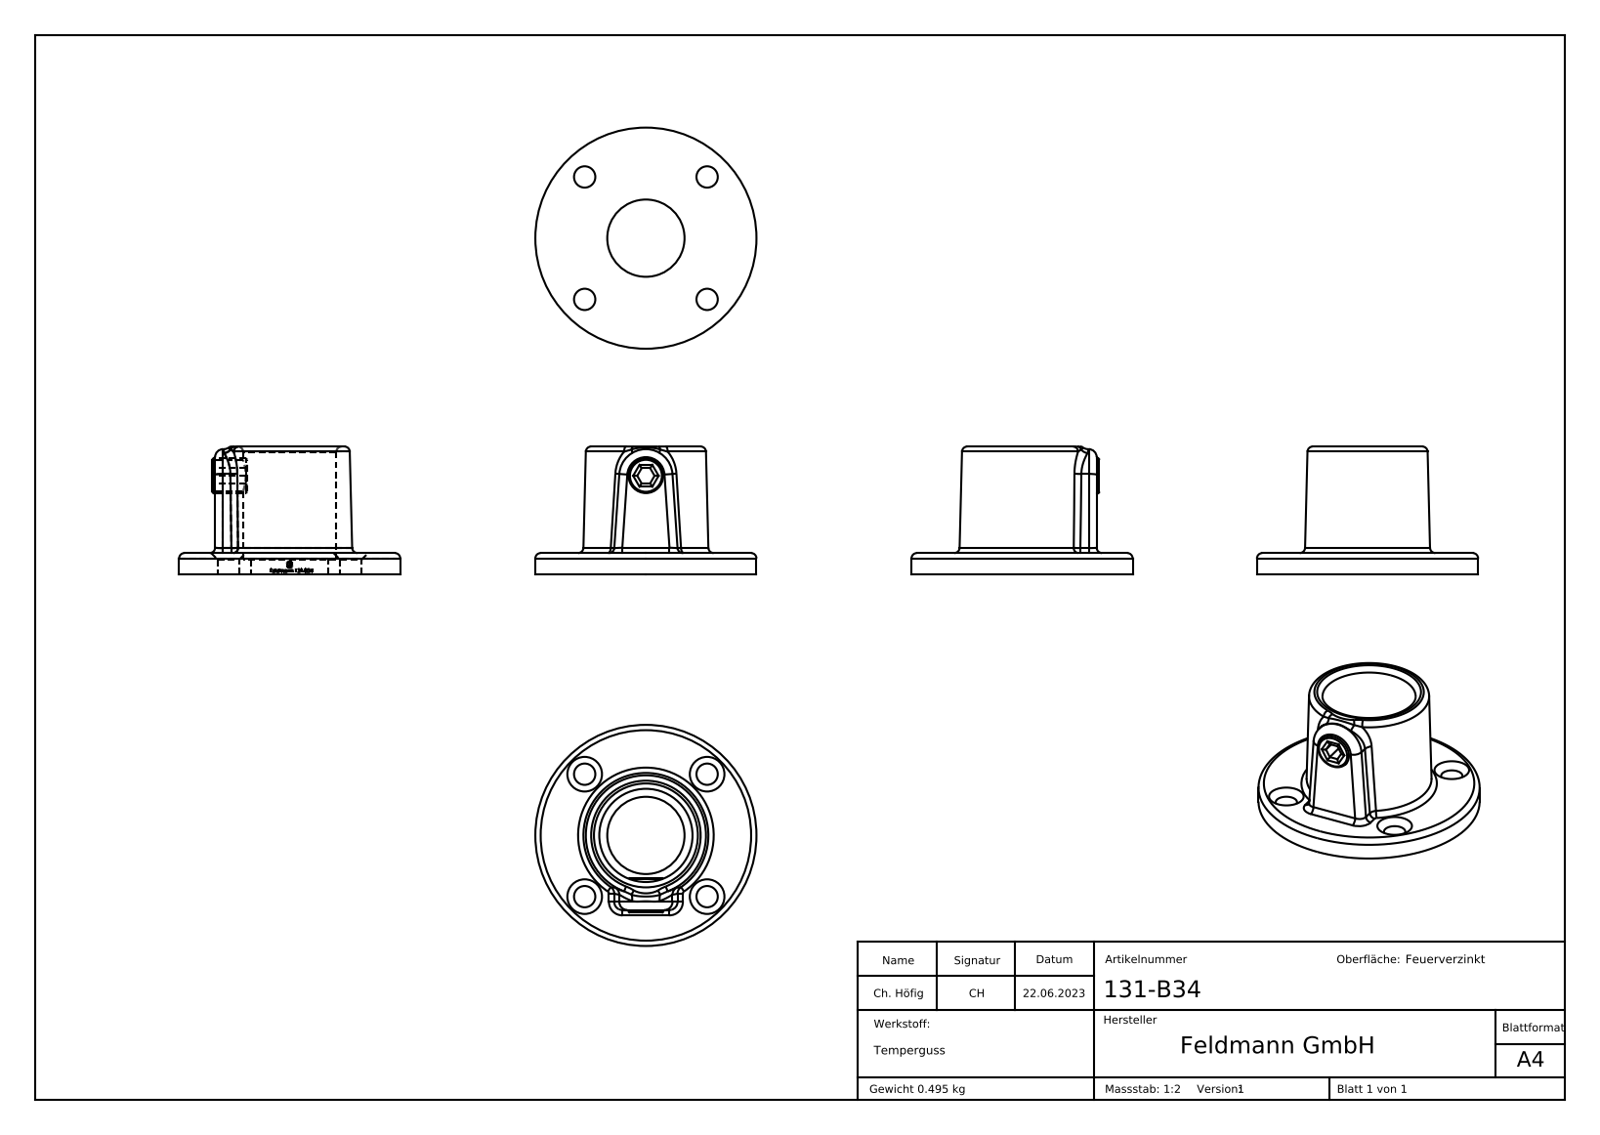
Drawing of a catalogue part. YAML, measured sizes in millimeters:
part_name: "131-B34 Teil2_131-B34 Teil2; 131-B34 Teil1_131-B34 Teil1; 131-B34"
step_written_by: "SolidWorks 2018 (CONFIG_CONTROL_DESIGN)"
units: millimeters
bodies: {solids: 2, faces: 313, planar: 135, cylindrical: 49, other: 129}
overall_size: [83, 83, 48]
volume: 67641
surface_area: 23628
round_holes:
  - {diameter: 8, count: 4}
  - {diameter: 11.8, count: 1}
  - {diameter: 29, count: 1}
  - {diameter: 35, count: 1}
round_bosses_or_shafts:
  - {diameter: 83, count: 1}
  - {diameter: 13, count: 1}
partial_cylinders:
  - {radius: 2, count: 15}
  - {radius: 3, count: 2}
  - {radius: 10, count: 1}
  - {radius: 14.6, count: 1}
face_to_face_distances: [8, 5.5, 2.5, 48, 42.5, 40, 5.62, 1, 12, 13]
hole_center_spacings: [32.5, 45.96, 65]
